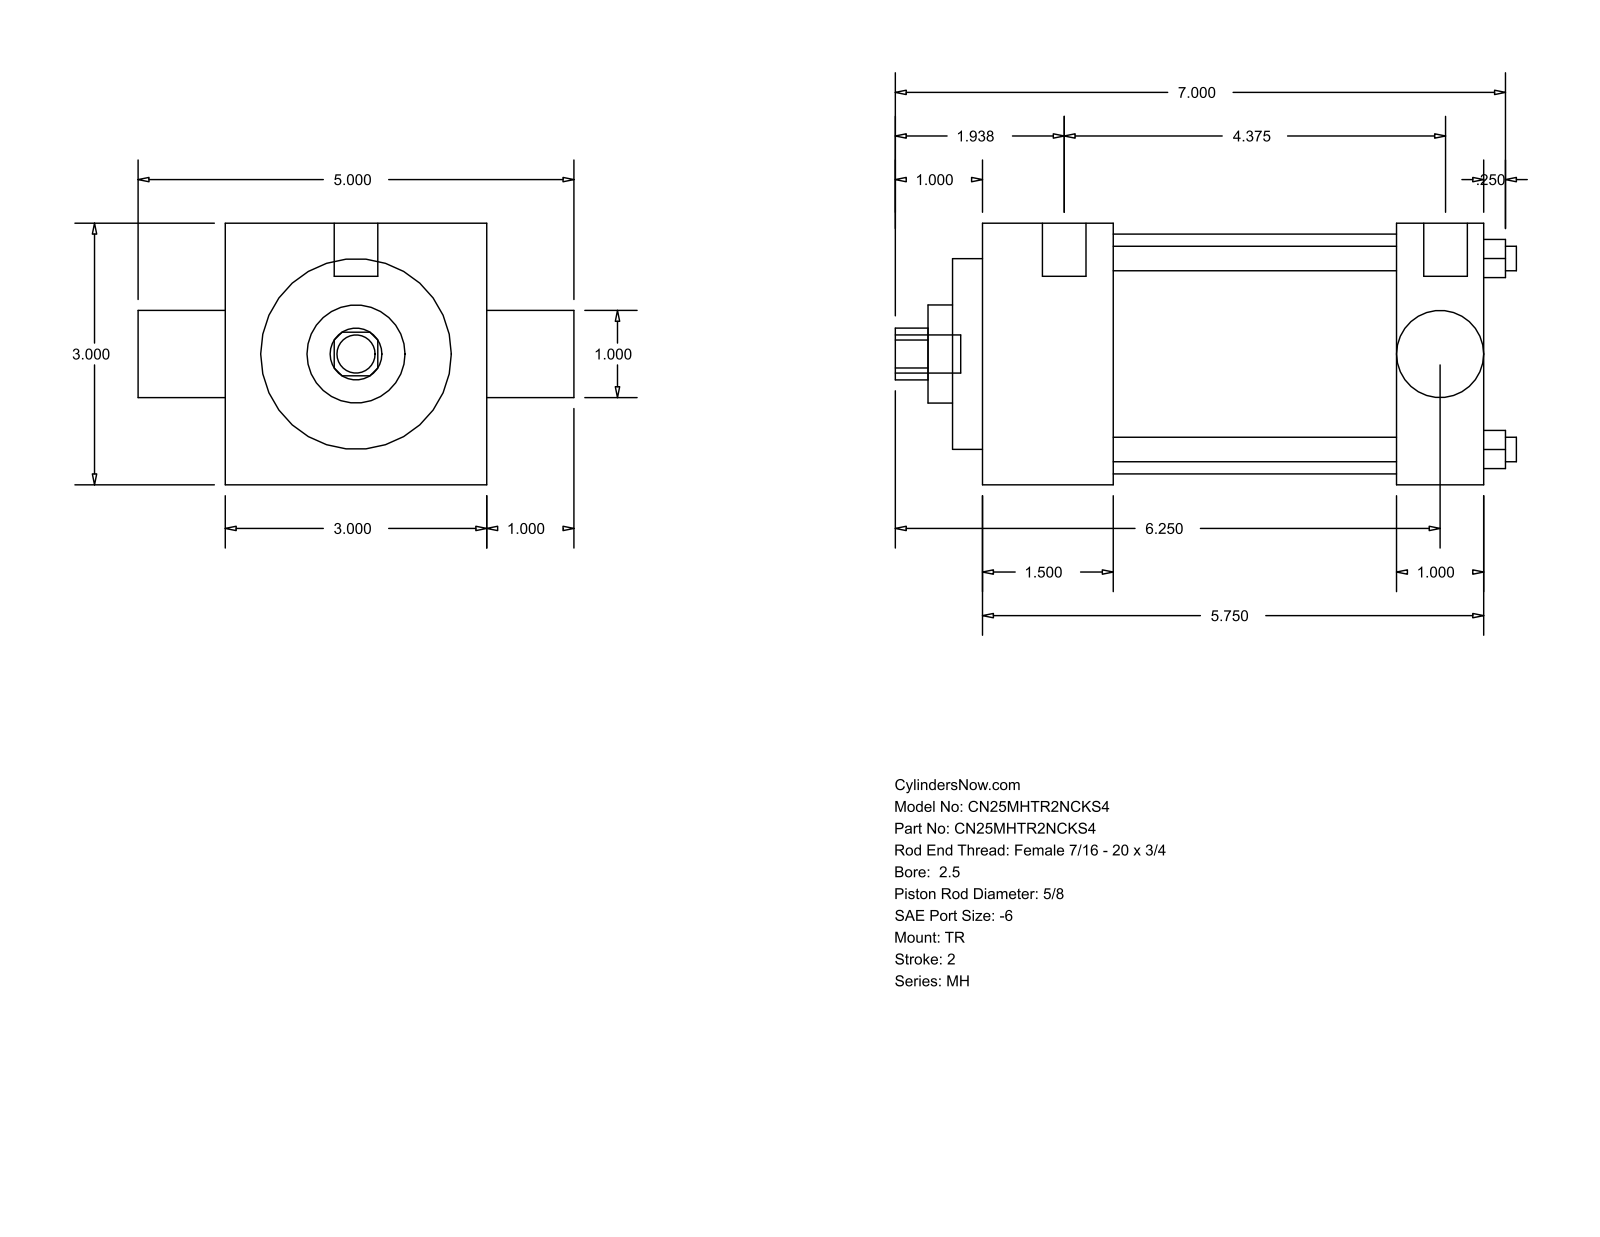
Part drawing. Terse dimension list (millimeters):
name: MH_TR__0250_0.625
written by: GSSL Pune (CONFIG_CONTROL_DESIGN)
unit: mm
bodies: 0 solids, 86 faces (61 planar, 25 cylindrical, 0 other)
size: 180.97 × 127 × 76.2
holes: 4× ⌀7.14, 1× ⌀15.88, 1× ⌀25.35, 1× ⌀28.57, 1× ⌀55.55, 1× ⌀69.85
bosses: 3× ⌀5.56, 2× ⌀12.7, 1× ⌀11.11
rounds: 1× R7.54
face distances: 76.2, 146.05, 25.4, 38.1, 107.95, 120.65, 82.55, 8.73, 46.83, 129.38
hole spacings: 39.33, 55.62, 78.66
